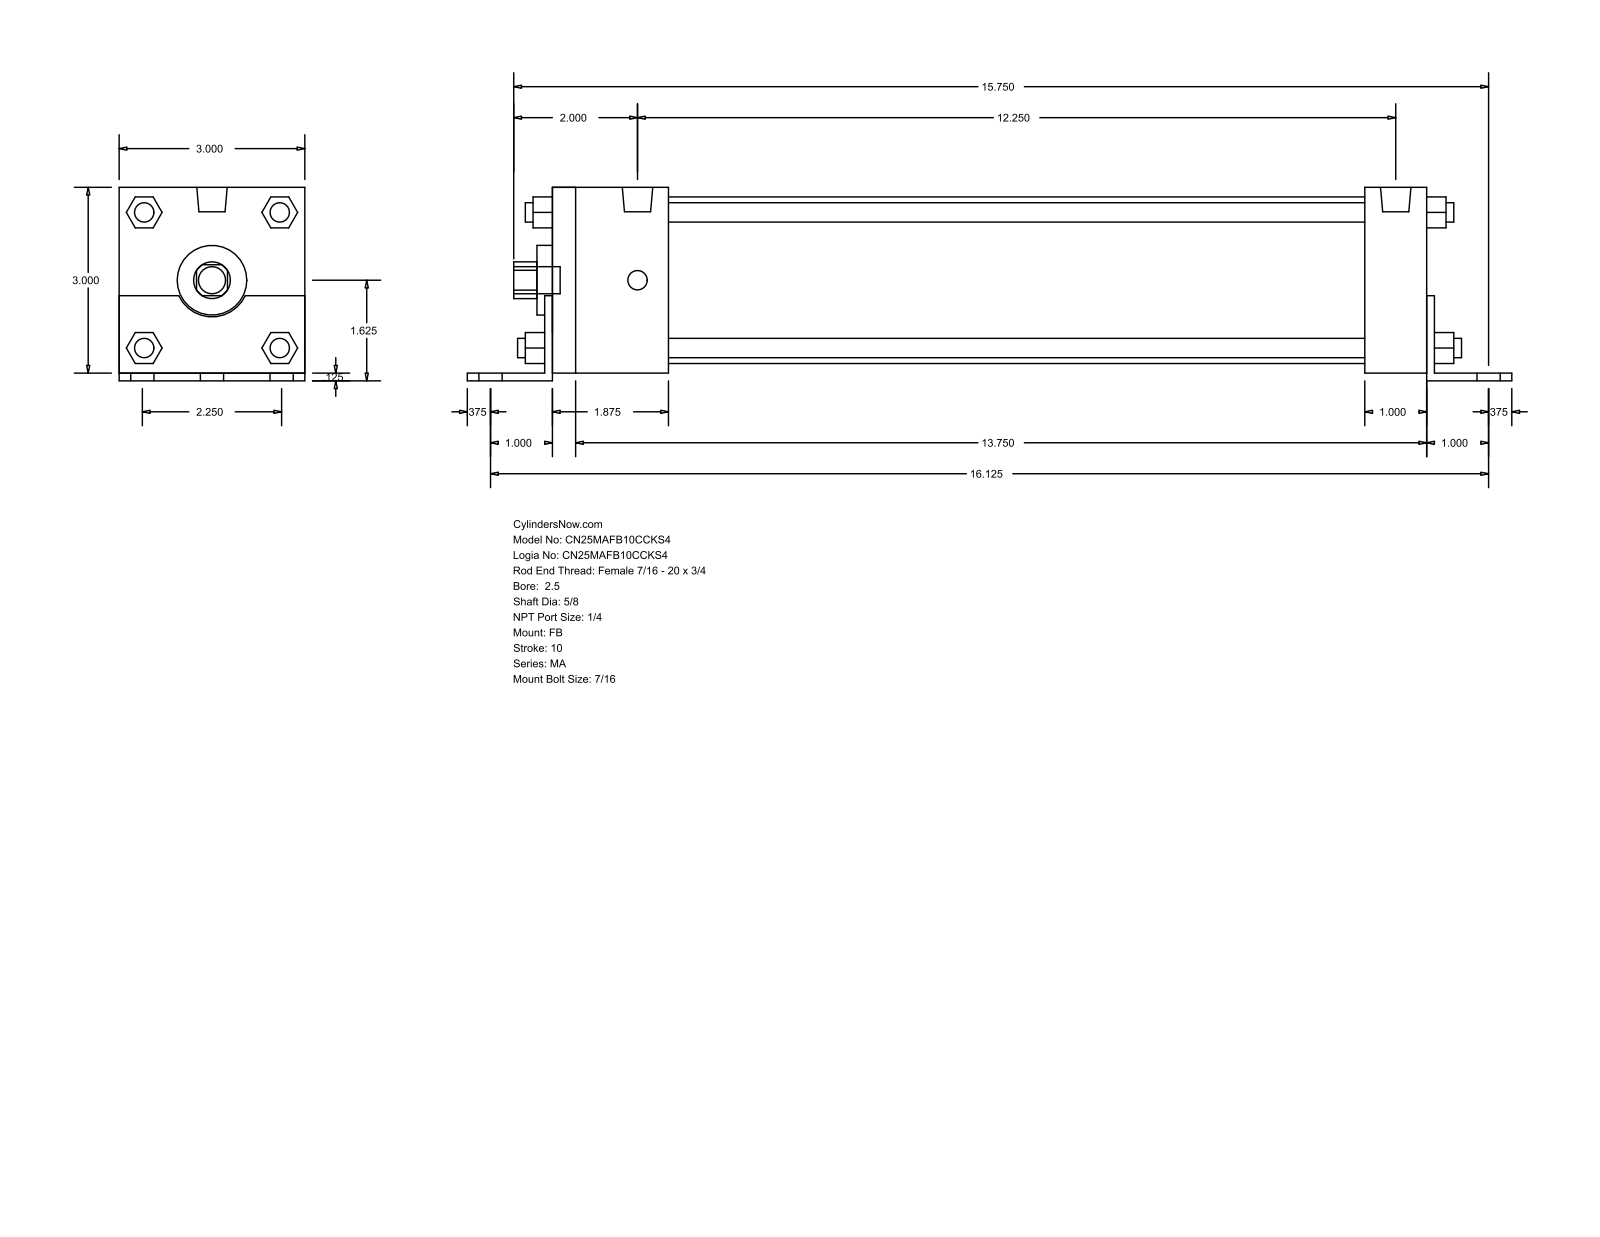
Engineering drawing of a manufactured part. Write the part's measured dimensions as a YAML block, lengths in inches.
part_name: "MA_FB__0250_0.625"
step_written_by: "GSSL Pune (CONFIG_CONTROL_DESIGN)"
units: inches
bodies: {solids: 0, faces: 140, planar: 105, cylindrical: 35, other: 0}
overall_size: [16.875, 3.125, 3]
round_holes:
  - {diameter: 0.625, count: 1}
  - {diameter: 1.125, count: 1}
  - {diameter: 2.69, count: 1}
round_bosses_or_shafts:
  - {diameter: 0.313, count: 8}
  - {diameter: 0.437, count: 7}
  - {diameter: 0.492, count: 2}
partial_cylinders:
  - {radius: 0.297, count: 1}
  - {radius: 0.593, count: 1}
face_to_face_distances: [3, 0.125, 3.125, 14.125, 14.375, 0.125, 14.25, 1.875, 1, 14.25]
